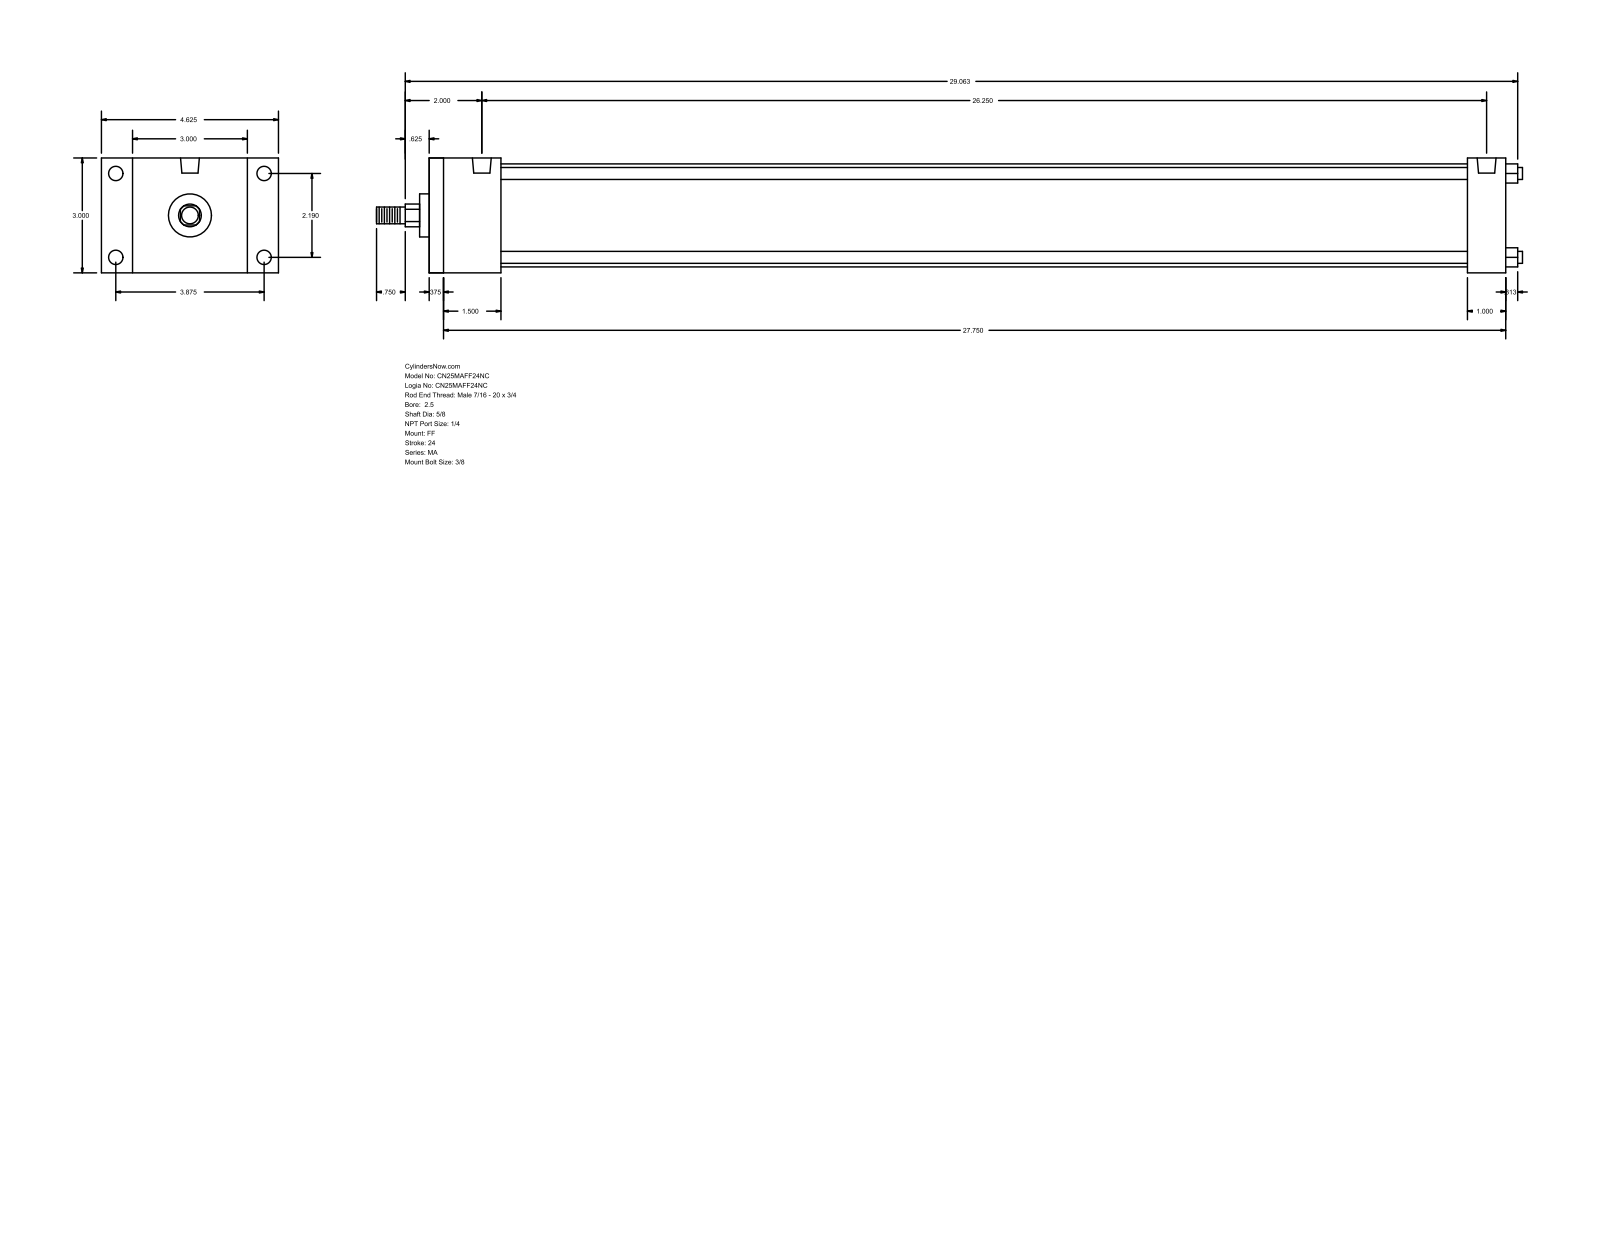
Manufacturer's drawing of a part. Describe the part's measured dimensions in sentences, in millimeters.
The part is named "MA_FF__0250_0.625". Its 3-D file was written by "GSSL Pune (CONFIG_CONTROL_DESIGN)". It is 0 solids with 92 faces: 64 planar, 28 cylindrical and 0 other. Overall it measures 760.41 by 117.47 by 76.2 millimeters. Round holes: 4 of diameter 7.94, 4 of diameter 9.53, 2 of diameter 12.49. Round bosses or shafts: 4 of diameter 7.94, 1 of diameter 68.33, 1 of diameter 28.57, 1 of diameter 15.88, 1 of diameter 11.11. Partial cylindrical surfaces (rounded edges, fillets, slot ends): 1 of radius 7.54. The main face-to-face distances are 76.2, 714.37, 704.85, 9.52, 25.4, 47.62, 688.97, 38.1, 679.45, 641.35. The hole center spacings are 55.62, 98.42, 113.05, 666.75.
